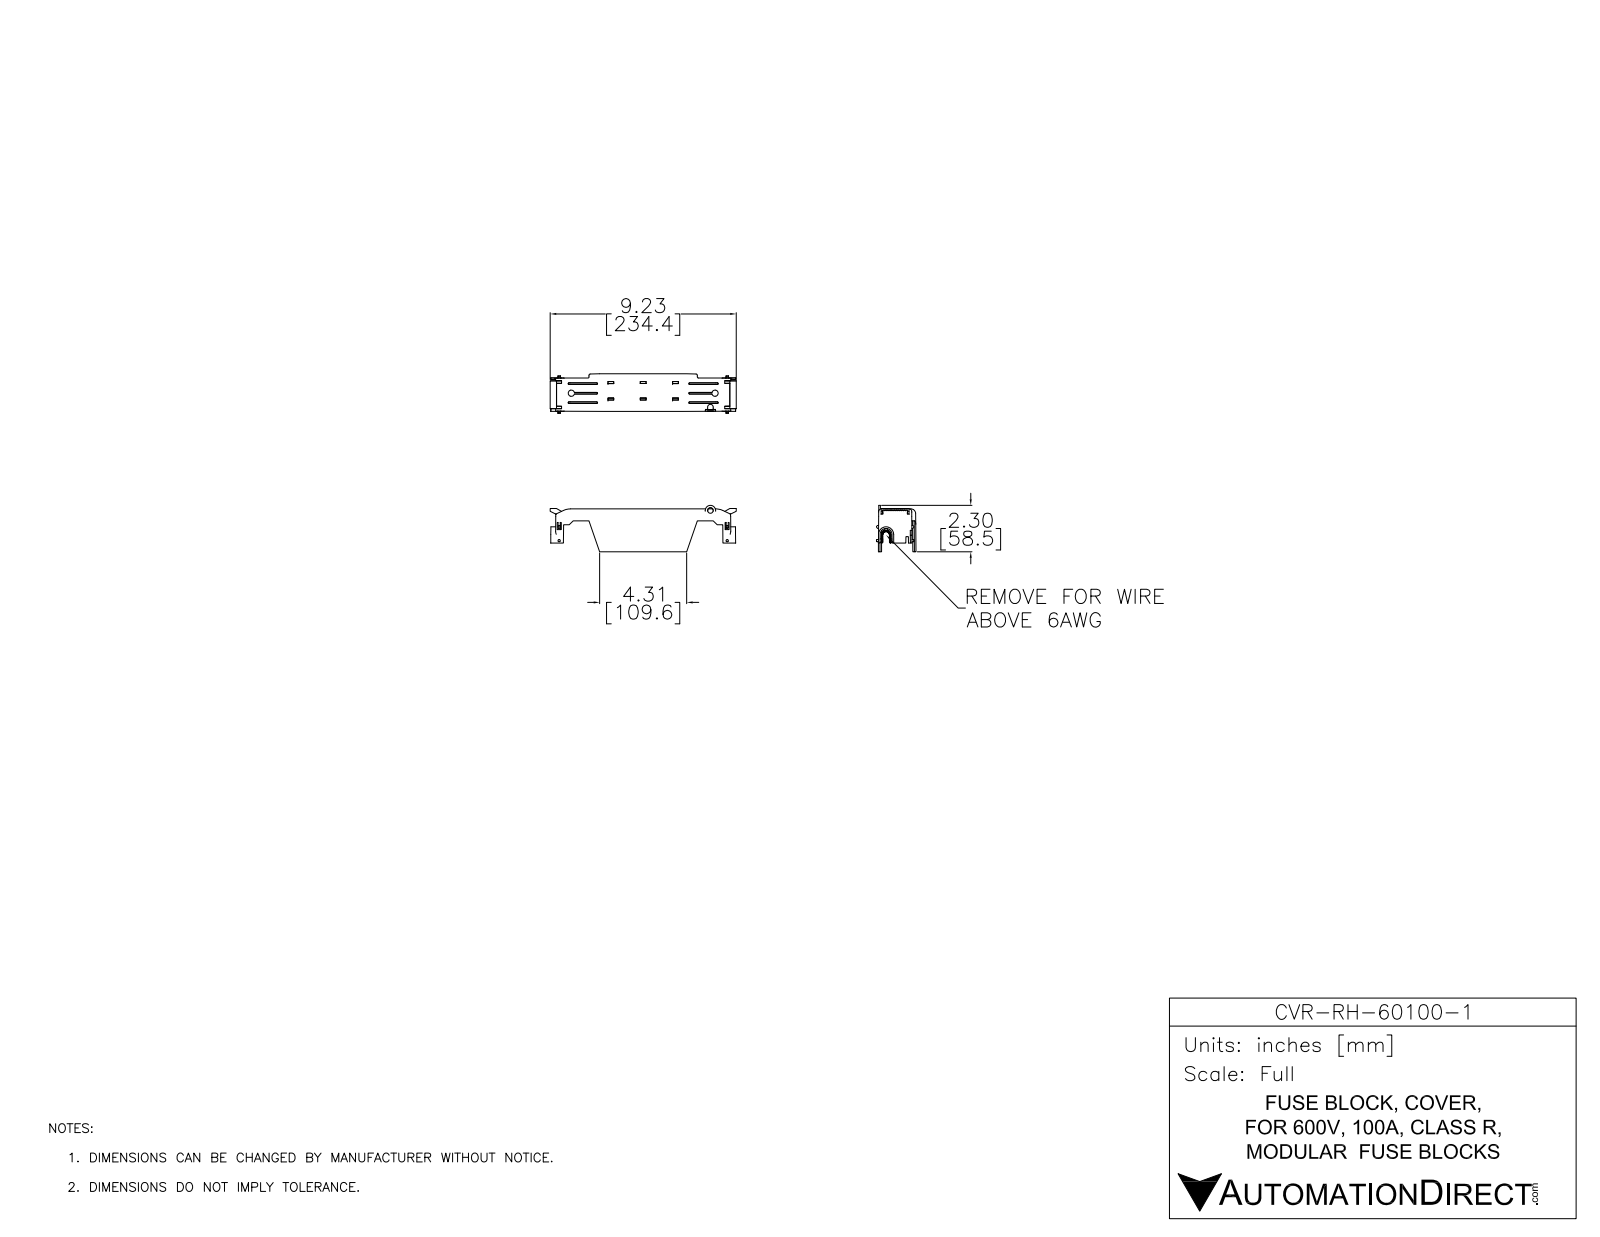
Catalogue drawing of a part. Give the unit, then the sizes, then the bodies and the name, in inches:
Units: inches
Overall size (bounding box): 9.23 × 2.304 × 1.964
Round holes (diameter × count): ⌀0.276 ×1
Partial cylindrical surfaces — rounded edges, fillets, slot ends (radius × count): R0.039 ×18, R0.118 ×14, R0.031 ×6, R0.059 ×4, R0.01 ×2, R0.02 ×2, R0.167 ×2, R0.63 ×2
Main face-to-face distances: 0.079, 0.197, 0.118, 0.276, 0.157, 0.803, 0.989, 1.068, 1.186, 1.265
Volume: 4.09 in³ · Surface area: 110.1 in²
Bodies: 1 solid, 1436 faces (948 planar, 102 cylindrical, 386 other)
Part name (STEP PRODUCT): CVR-RH-60100-1
STEP written by: SolidWorks 2017 (AUTOMOTIVE_DESIGN)
